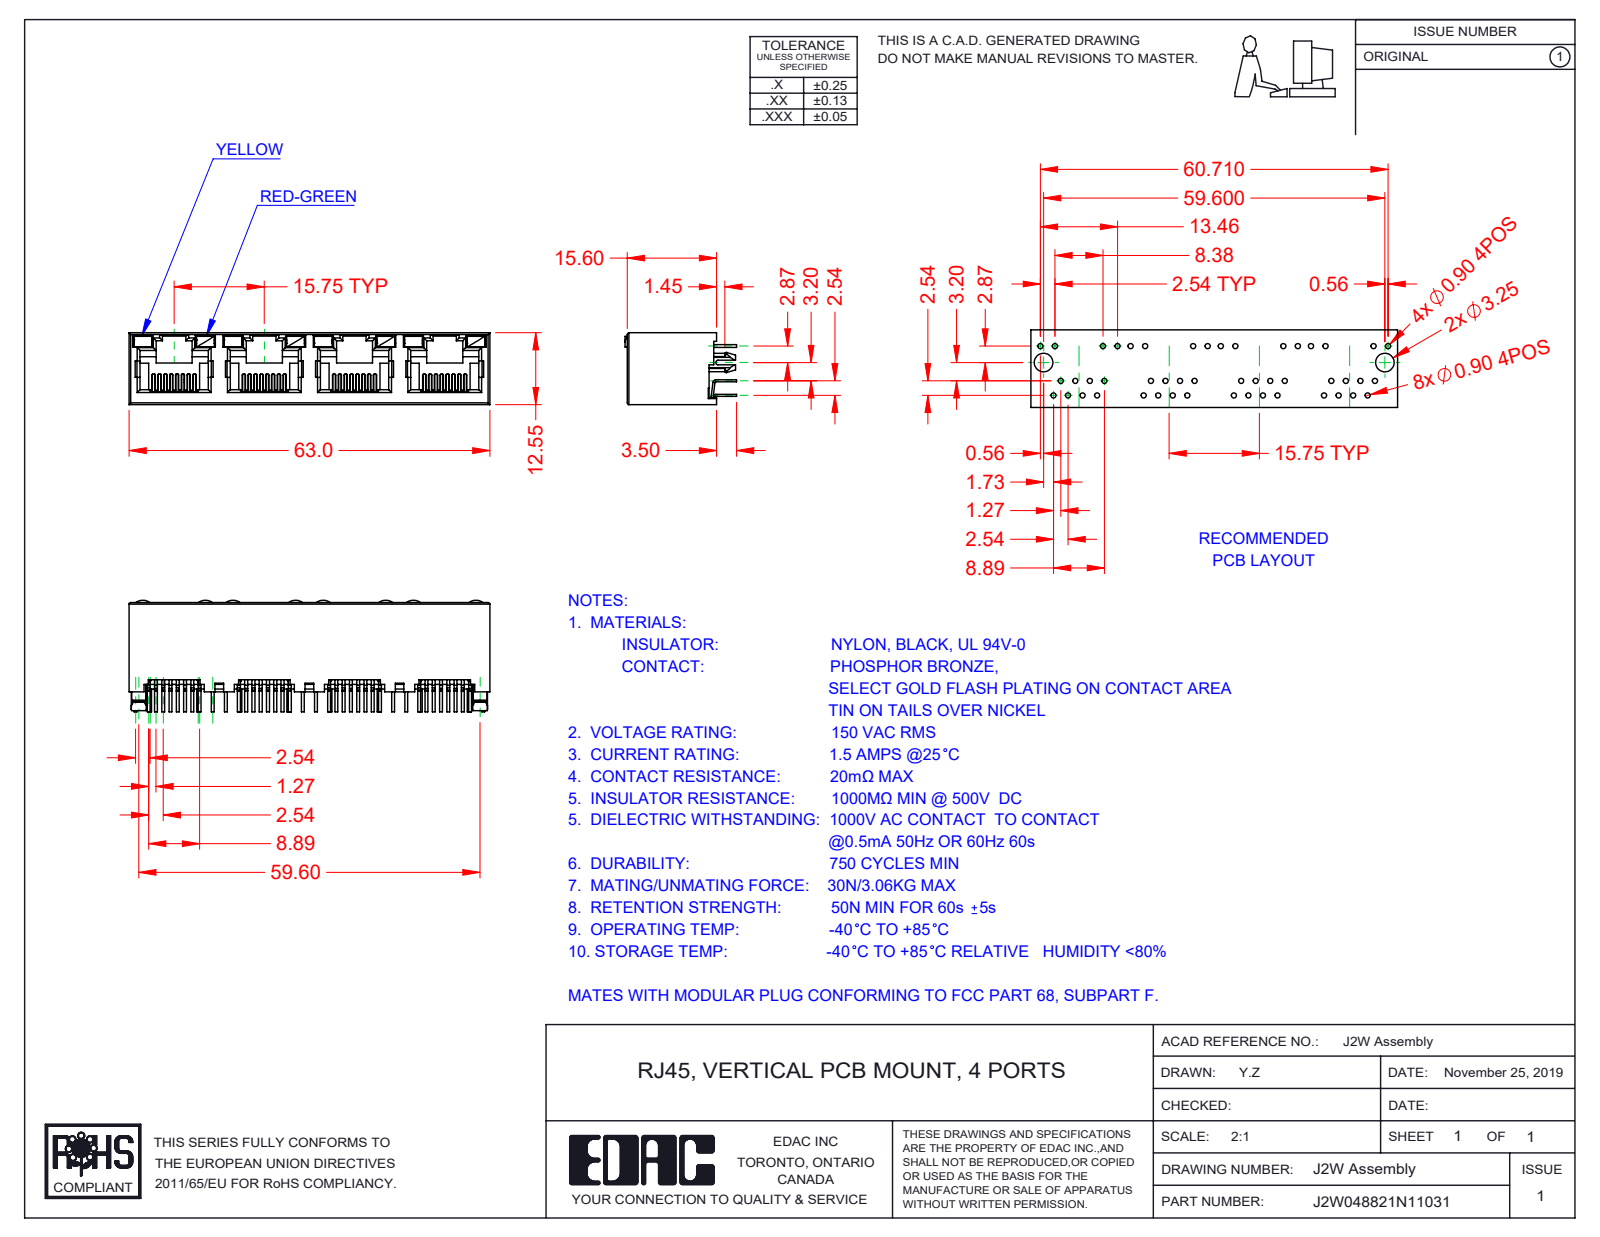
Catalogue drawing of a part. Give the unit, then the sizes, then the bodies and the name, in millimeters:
Units: millimetres
Overall size (bounding box): 63 × 19.5 × 12.55
Partial cylindrical surfaces — rounded edges, fillets, slot ends (radius × count): R0.15 ×64, R0.2 ×29, R0.5 ×28, R0.3 ×14, R0.45 ×8, R2 ×8, R0.25 ×2, R1.5 ×2
Main face-to-face distances: 12.55, 11.9, 0.65, 15.75, 0.36, 1.5, 0.78, 0.6, 11.3, 31.5
Volume: 5 335 mm³ · Surface area: 13 144 mm²
Bodies: 45 solids, 3139 faces (2600 planar, 481 cylindrical, 58 other)
Part name (STEP PRODUCT): 2W Insulator; J2W048821N16131; 2W Contacts; 2W Contact Lock (+2 more)
STEP written by: SolidWorks 2016 (CONFIG_CONTROL_DESIGN)
